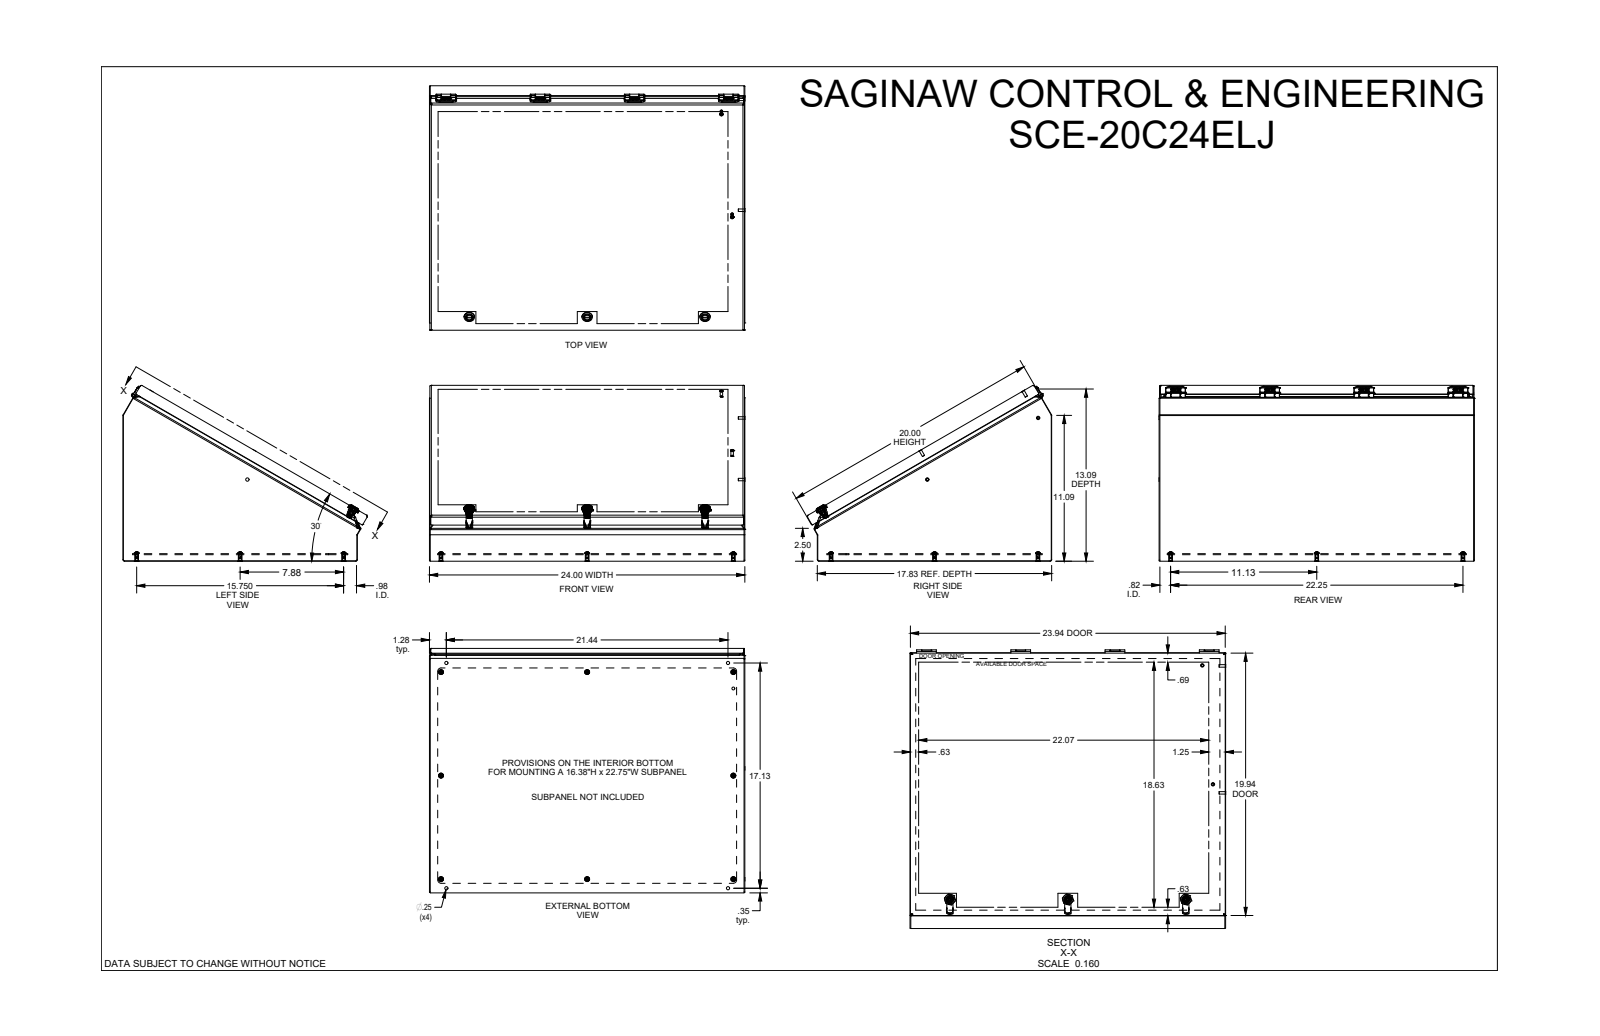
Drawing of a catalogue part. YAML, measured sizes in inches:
part_name: "SCE-20C24ELJ"
step_written_by: "SolidWorks 2019 (AUTOMOTIVE_DESIGN)"
units: inches
bodies: {solids: 48, faces: 1780, planar: 688, cylindrical: 722, other: 370}
overall_size: [24.004, 18.594, 13.38]
volume: 137
surface_area: 4295
round_holes:
  - {diameter: 0.25, count: 12}
  - {diameter: 0.19, count: 8}
  - {diameter: 0.281, count: 8}
  - {diameter: 0.02, count: 4}
  - {diameter: 0.1, count: 4}
  - {diameter: 0.174, count: 4}
  - {diameter: 0.193, count: 4}
  - {diameter: 0.266, count: 4}
  - {diameter: 0.2, count: 3}
  - {diameter: 0.239, count: 3}
  - {diameter: 0.254, count: 3}
  - {diameter: 0.269, count: 3}
round_bosses_or_shafts:
  - {diameter: 0.28, count: 8}
  - {diameter: 0.26, count: 4}
  - {diameter: 0.256, count: 4}
  - {diameter: 0.188, count: 4}
  - {diameter: 0.18, count: 4}
  - {diameter: 0.788, count: 3}
  - {diameter: 0.548, count: 3}
  - {diameter: 0.46, count: 3}
partial_cylinders:
  - {radius: 0.03, count: 48}
  - {radius: 0.013, count: 41}
  - {radius: 0.01, count: 30}
  - {radius: 0.06, count: 26}
  - {radius: 0.015, count: 24}
  - {radius: 0.02, count: 17}
  - {radius: 0.12, count: 16}
  - {radius: 0.063, count: 12}
face_to_face_distances: [0.06, 0.06, 0.075, 0.436, 0.496, 0.511, 0.571, 23.94, 23.88, 24]
hole_center_spacings: [7.167, 14.333, 7.167, 21.5, 0.802, 7.875, 8.576, 10.741]
